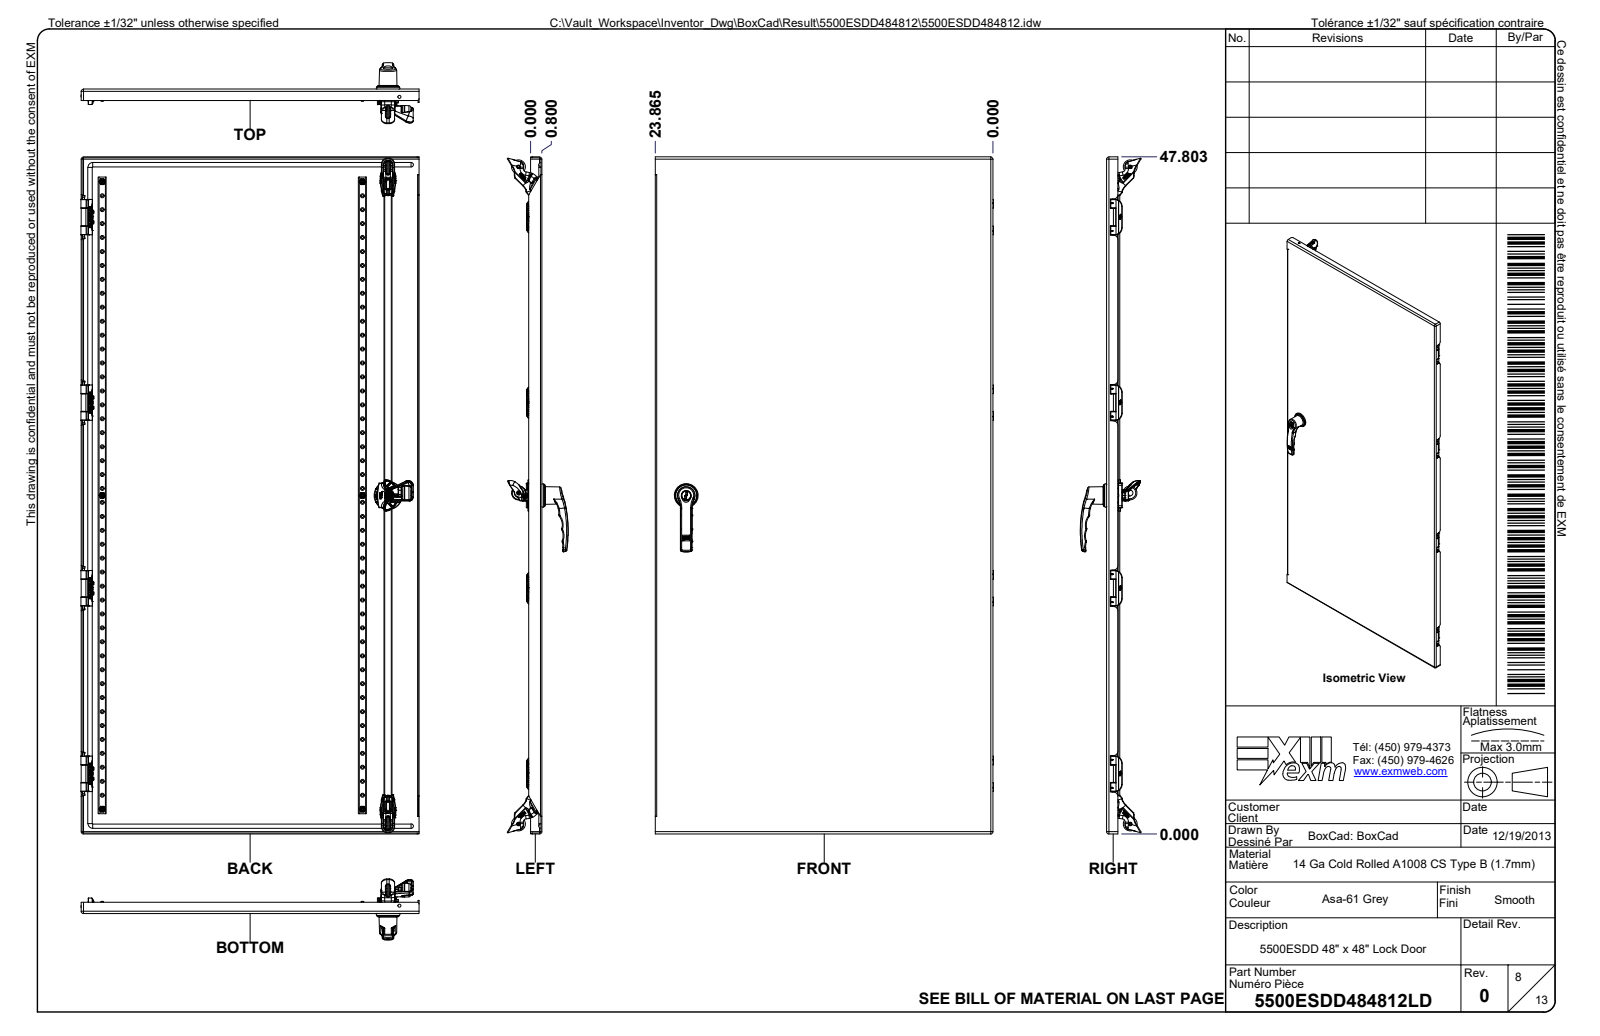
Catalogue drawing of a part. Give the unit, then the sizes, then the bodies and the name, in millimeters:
Units: millimetres
Overall size (bounding box): 1220.1 × 1219.2 × 380.6
Round holes (diameter × count): ⌀4.2 ×176, ⌀1.1 ×24, ⌀0.8 ×23, ⌀8 ×20, ⌀5.1 ×17, ⌀7.9 ×15, ⌀5 ×12, ⌀6.8 ×12, ⌀4.2 ×10, ⌀4.5 ×8, ⌀6.9 ×8, ⌀7.7 ×6
Round bosses / shafts (diameter × count): ⌀6 ×176, ⌀1 ×24, ⌀0.8 ×23, ⌀5.9 ×18, ⌀9.5 ×12, ⌀4.5 ×12, ⌀18.2 ×8, ⌀7.9 ×8
Partial cylindrical surfaces — rounded edges, fillets, slot ends (radius × count): R0.5 ×471, R0.3 ×358, R1 ×299, R0.2 ×232, R0.4 ×119, R0.8 ×77, R0.1 ×68, R2 ×67
Main face-to-face distances: 1.7, 331.5, 329.8, 1217.5, 333.2, 23.9, 22.2, 307.6, 309.3, 26.6
Hole centre spacings: 332.8, 665.5, 10, 562, 591.2, 1152.9, 1256.6, 1295
Volume: 12 960 000 mm³ · Surface area: 13 340 000 mm²
Bodies: 161 solids, 25468 faces (6157 planar, 6921 cylindrical, 12390 other)
Part name (STEP PRODUCT): 5500ESDD484812; 5500ESDD484812B; 5500ESDD484812B-P; STK-Q-16005 (+8 more)
STEP written by: Autodesk Inventor 2024 (AUTOMOTIVE_DESIGN)
